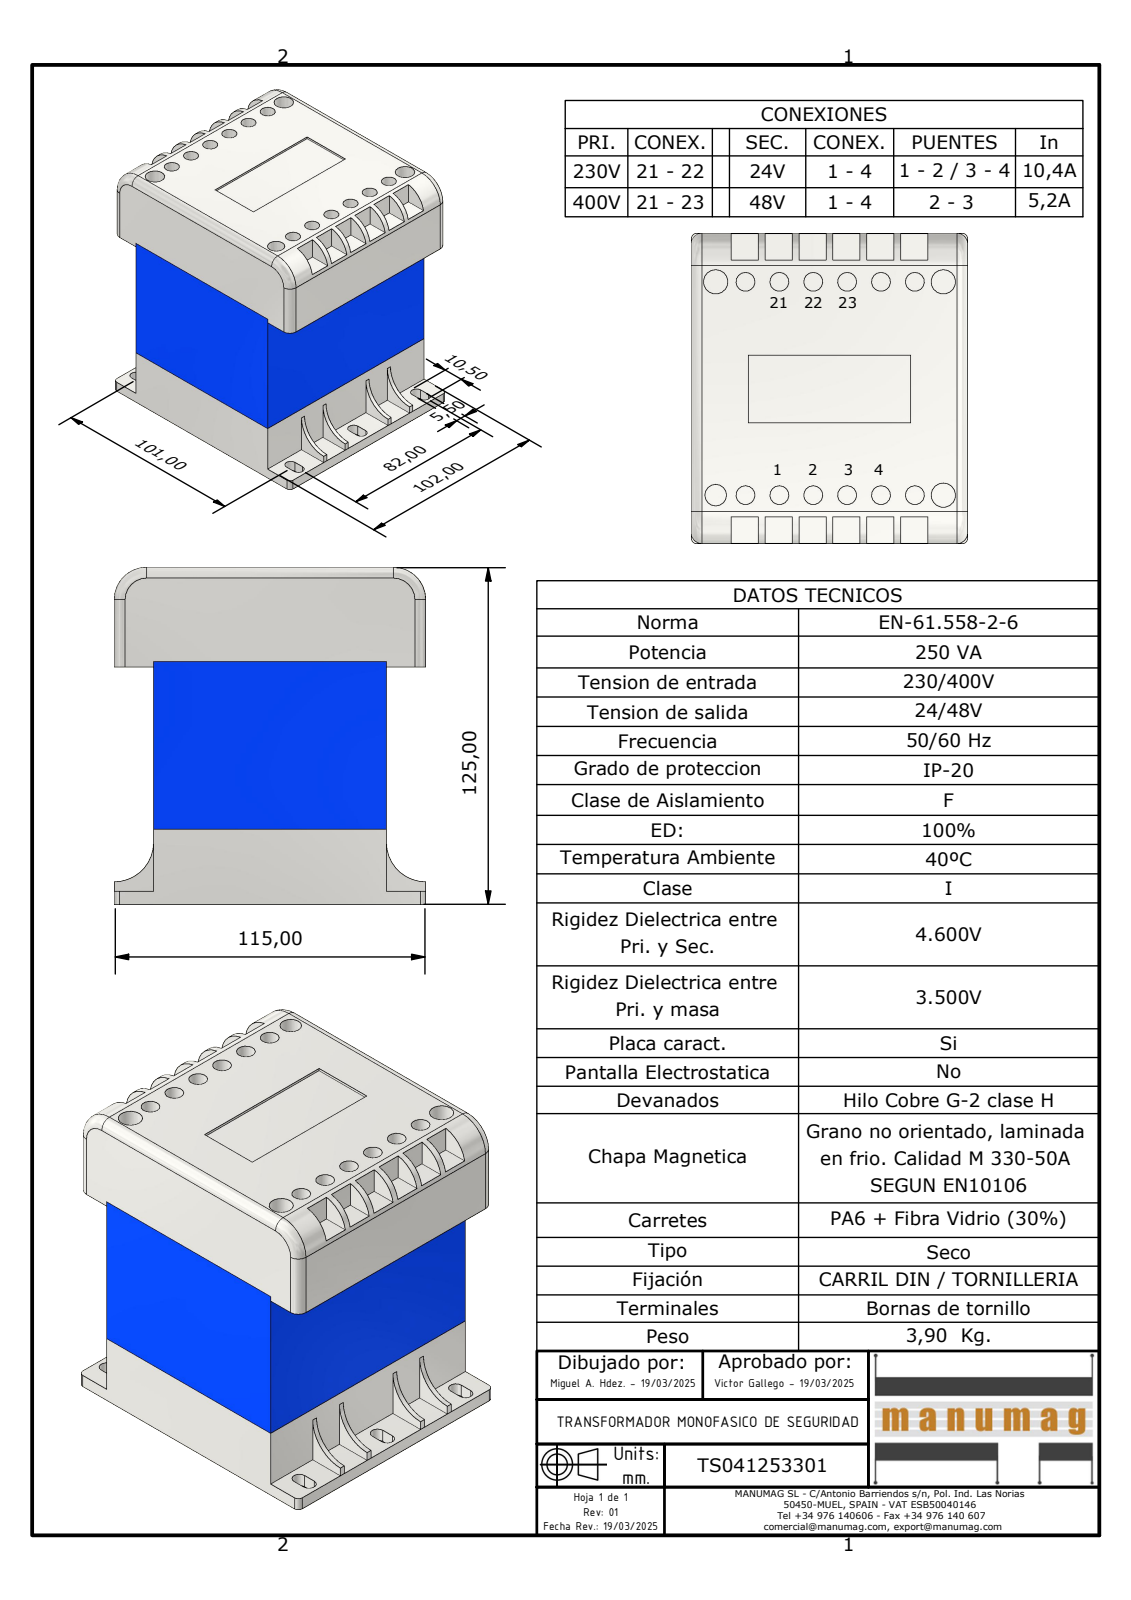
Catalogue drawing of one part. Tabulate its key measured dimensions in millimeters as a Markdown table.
| quantity | value |
| --- | --- |
| part name | TS041253301; INFERIOR EI96; CENTRAL EI96-60; SUPERIOR EI96 |
| STEP written by | Autodesk Inventor 2023 (AUTOMOTIVE_DESIGN) |
| units | millimeters |
| bodies | 11 solids, 200 faces (152 planar, 44 cylindrical, 4 other) |
| overall size | 125 × 115 × 102 |
| volume | 483 000 mm³ |
| surface area | 136 147 mm² |
| round holes (diameter × count) | 7 × 12, 9 × 3, 8 × 1 |
| partial cylindrical surfaces (radius × count) | 2.5 × 8, 4 × 6, 2 × 4, 12 × 2, 14.5 × 2 |
| main face-to-face distances | 1, 85, 101, 5, 102, 90, 86, 84, 100, 35 |
| hole center spacings | 12.5, 79.98, 25, 79, 82.86, 37.5, 87.45, 50 |
